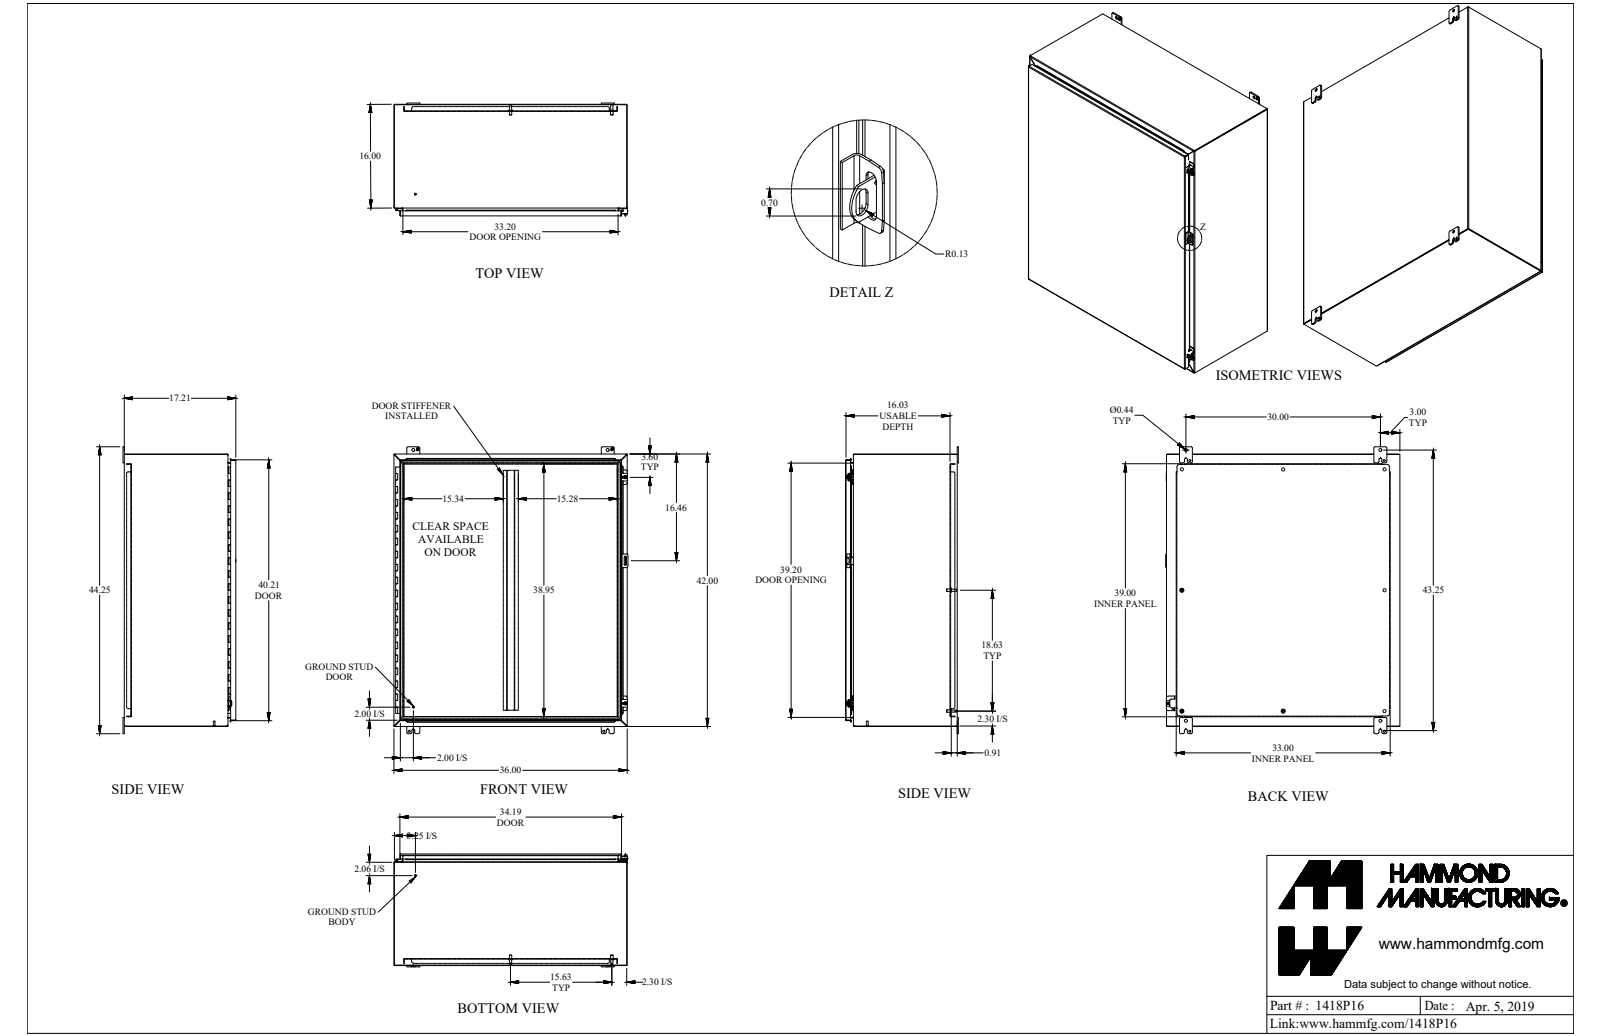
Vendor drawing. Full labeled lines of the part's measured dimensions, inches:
Part name (STEP PRODUCT): 1418P16_Default
STEP written by: SolidWorks 2019 (CONFIG_CONTROL_DESIGN)
Units: inches
Bodies: 52 solids, 1548 faces (883 planar, 556 cylindrical, 109 other)
Overall size (bounding box): 44.25 × 36.125 × 17.437
Volume: 615.4 in³ · Surface area: 16 096 in²
Round holes (diameter × count): ⌀0.5 ×8, ⌀0.307 ×4, ⌀0.313 ×4, ⌀0.437 ×4, ⌀0.445 ×4, ⌀0.213 ×2, ⌀0.265 ×2, ⌀0.375 ×2, ⌀0.125 ×1, ⌀0.187 ×1
Round bosses / shafts (diameter × count): ⌀0.65 ×8, ⌀0.375 ×8, ⌀0.33 ×8, ⌀1 ×4, ⌀0.5 ×2, ⌀0.39 ×2, ⌀0.281 ×2, ⌀0.25 ×2
Partial cylindrical surfaces — rounded edges, fillets, slot ends (radius × count): R0.188 ×37, R0.036 ×22, R0.108 ×22, R0.25 ×20, R0.116 ×16, R0.048 ×13, R0.143 ×13, R0.04 ×8
Main face-to-face distances: 0.072, 17.113, 17.041, 17.185, 0.095, 0.937, 35.928, 1.009, 16.081, 16.009
Hole centre spacings: 15.625, 18.625, 30, 31.25, 36.38, 37.25, 40.394, 1.735
